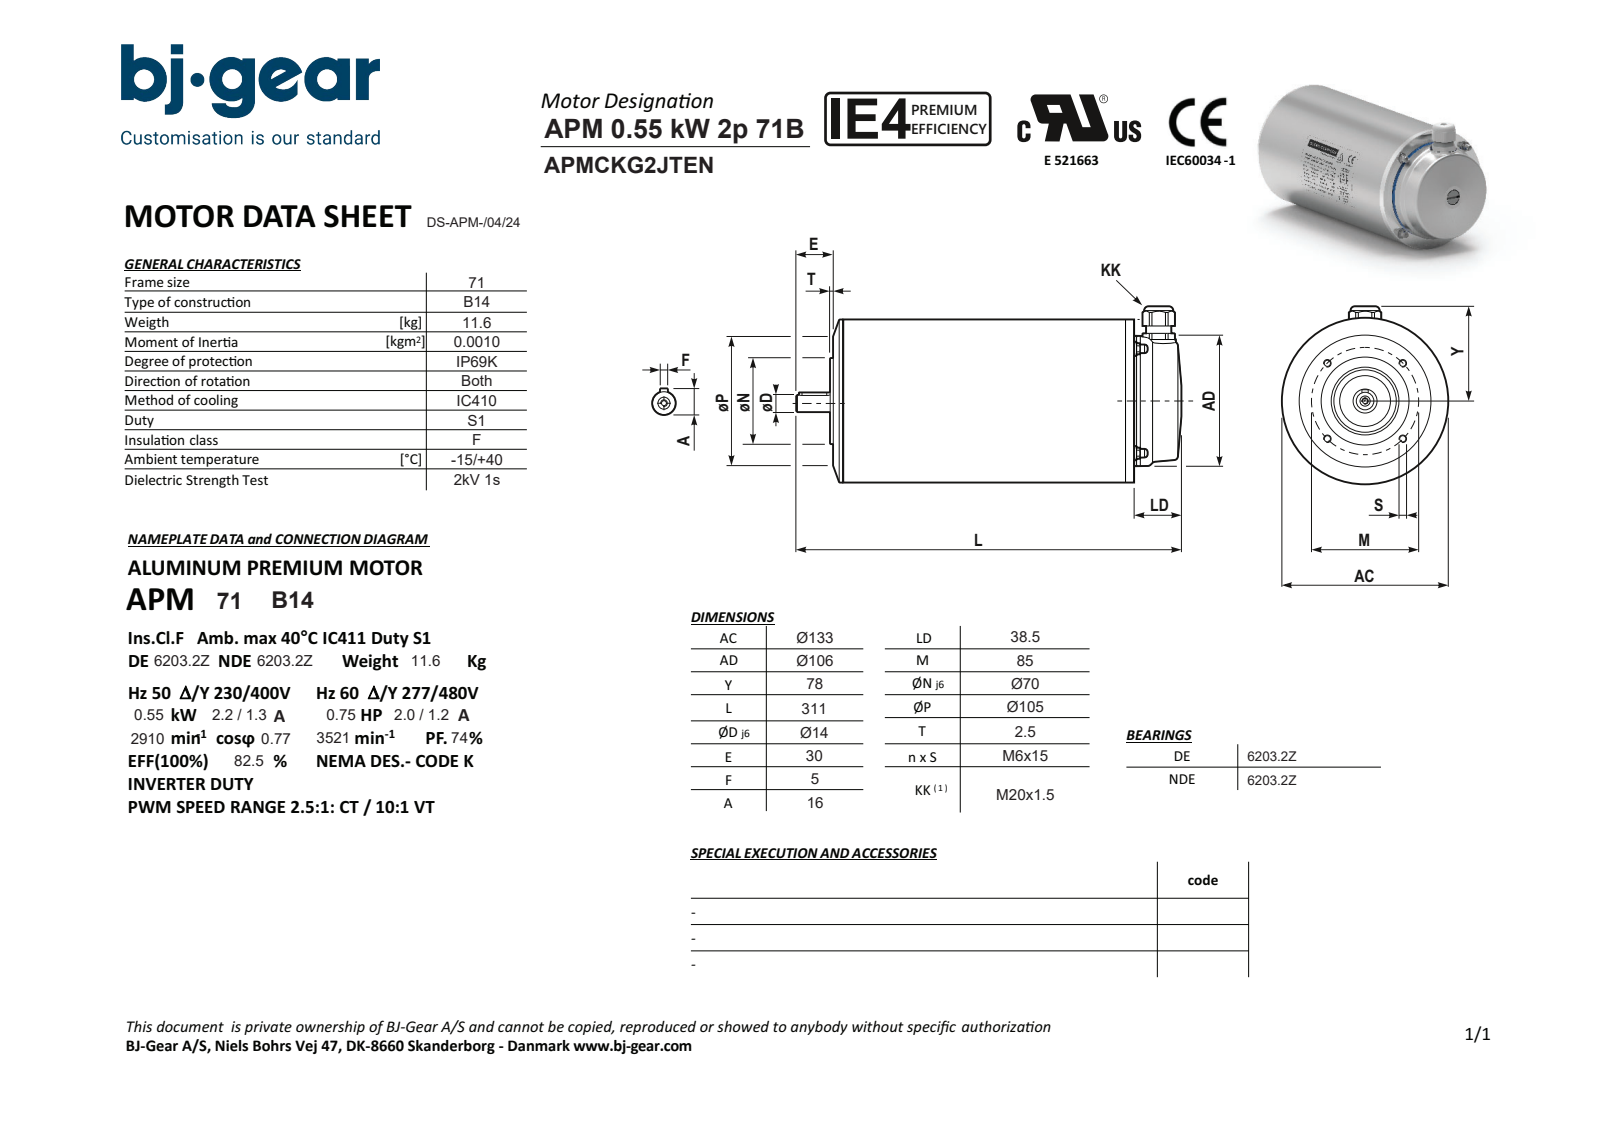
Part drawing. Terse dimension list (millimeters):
name: APMCKG2JTENN4KCR2-N---NNN
written by: Solid Edge (AUTOMOTIVE_DESIGN)
unit: mm
bodies: 1 solid, 156 faces (71 planar, 50 cylindrical, 35 other)
size: 311 × 143.3 × 132.6
volume: 3 639 000 mm³; area: 145 191 mm²
holes: 4× ⌀4.92, 1× ⌀4.13, 1× ⌀5.3, 1× ⌀16, 1× ⌀28, 1× ⌀52
bosses: 4× ⌀11.5, 4× ⌀7, 1× ⌀132.6, 1× ⌀132.6, 1× ⌀106, 1× ⌀70, 1× ⌀23.7, 1× ⌀20.6
rounds: 2× R2.5, 1× R13.2
face distances: 242.5, 237, 5.5, 8, 2.5, 245, 283.5, 38.5, 275.5, 281
hole spacings: 42.5, 60.1, 84.99
